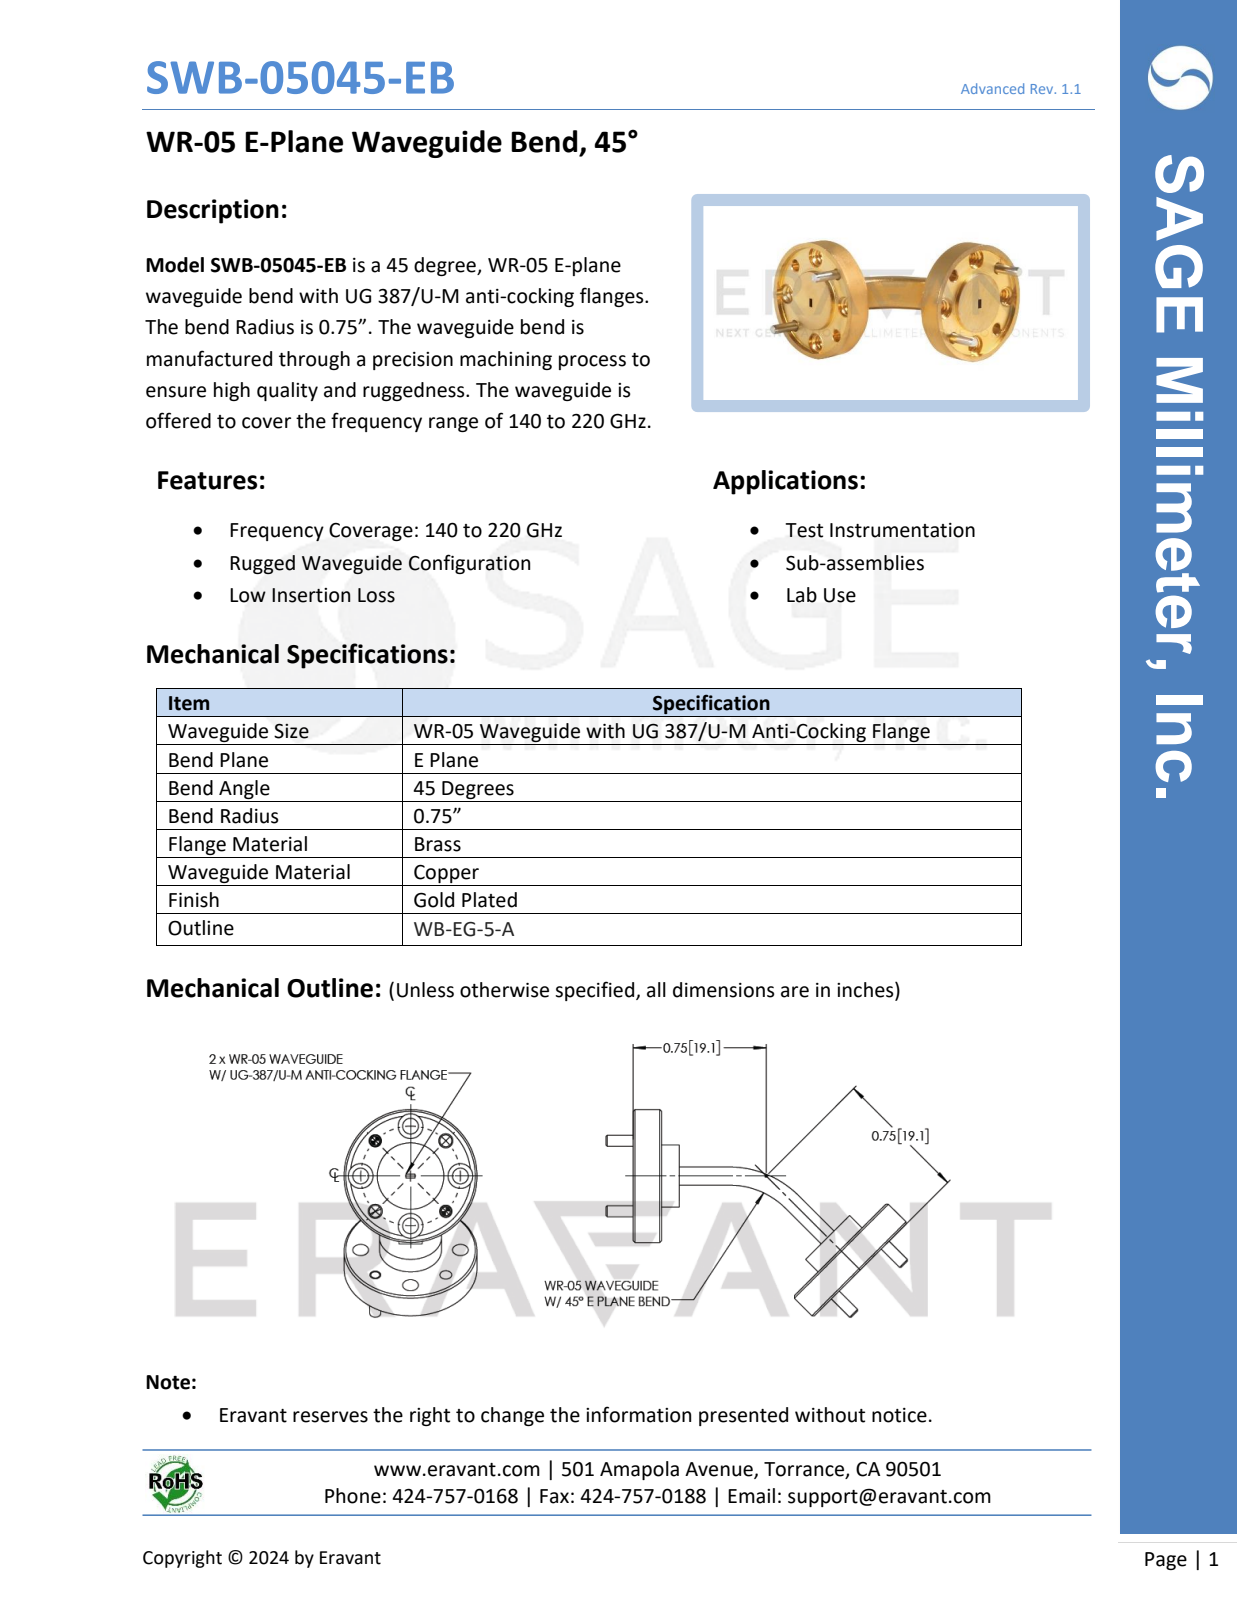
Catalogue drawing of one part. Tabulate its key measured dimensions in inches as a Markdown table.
| quantity | value |
| --- | --- |
| part name | WB-EG-5-A, defeatured_02 |
| STEP written by | SolidWorks 2021 (AUTOMOTIVE_DESIGN) |
| units | inches |
| bodies | 5 solids, 160 faces (42 planar, 78 cylindrical, 40 other) |
| overall size | 1.699 × 1.171 × 0.75 |
| volume | 0.151 in³ |
| surface area | 3.948 in² |
| round holes (diameter × count) | 0.089 × 8, 0.14 × 8, 0.061 × 4, 0.067 × 4, 0.68 × 2 |
| round bosses / shafts (diameter × count) | 0.063 × 4, 0.75 × 2, 0.35 × 2, 0.375 × 1, 0.375 × 1 |
| partial cylindrical surfaces (radius × count) | 0.449 × 1, 0.551 × 1 |
| main face-to-face distances | 0.16, 0.1, 0.14, 0.13, 0.26, 0.02, 0.03, 0.131, 0.24, 0.23 |
| hole center spacings | 0.215, 0.281, 0.398, 0.52, 0.519, 0.562, 0.281, 0.398 |
